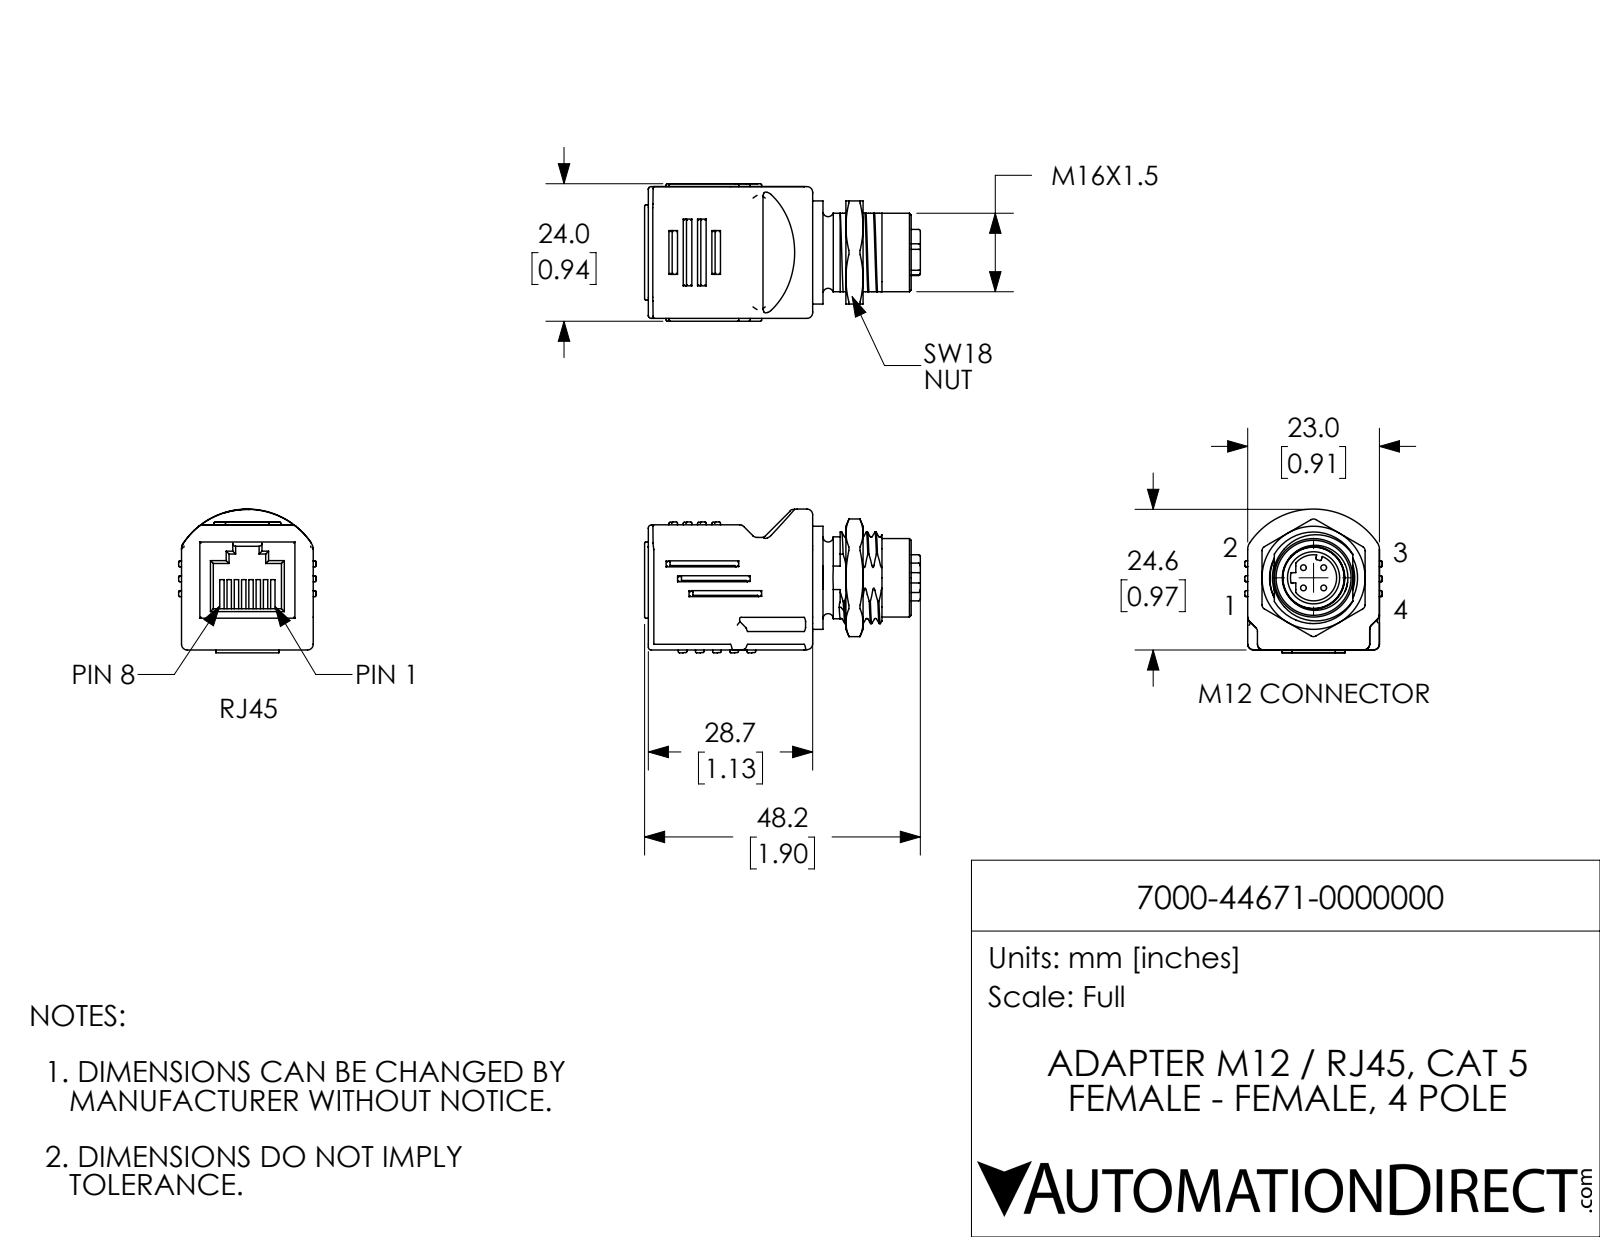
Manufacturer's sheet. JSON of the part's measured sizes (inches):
{"part_name": "7000-44671-0000000", "step_written_by": "SolidWorks 2017 (AUTOMOTIVE_DESIGN)", "units": "inches", "bodies": {"solids": 1, "faces": 697, "planar": 253, "cylindrical": 266, "other": 178}, "overall_size": [1.896, 0.988, 0.945], "volume_in3": 0.944, "surface_area_in2": 11.13, "round_holes": [[0.039, 4], [0.372, 1], [0.394, 1], [0.425, 1], [0.43, 1], [0.566, 1]], "round_bosses_or_shafts": [[0.709, 1], [0.563, 1], [0.539, 1], [0.421, 1], [0.37, 1], [0.317, 1], [0.295, 1], [0.294, 1]], "partial_cylinders_radius": [[0.008, 89], [0.039, 48], [0.02, 10], [0.012, 6], [0.031, 6], [0.079, 4], [0.531, 2], [0.315, 1]], "face_to_face_distances": [0.906, 1.13, 0.219, 0.118, 0.687, 0.86, 0.283, 0.577, 0.709, 0.228], "hole_center_spacings": [0.098, 0.139, 0.197]}
